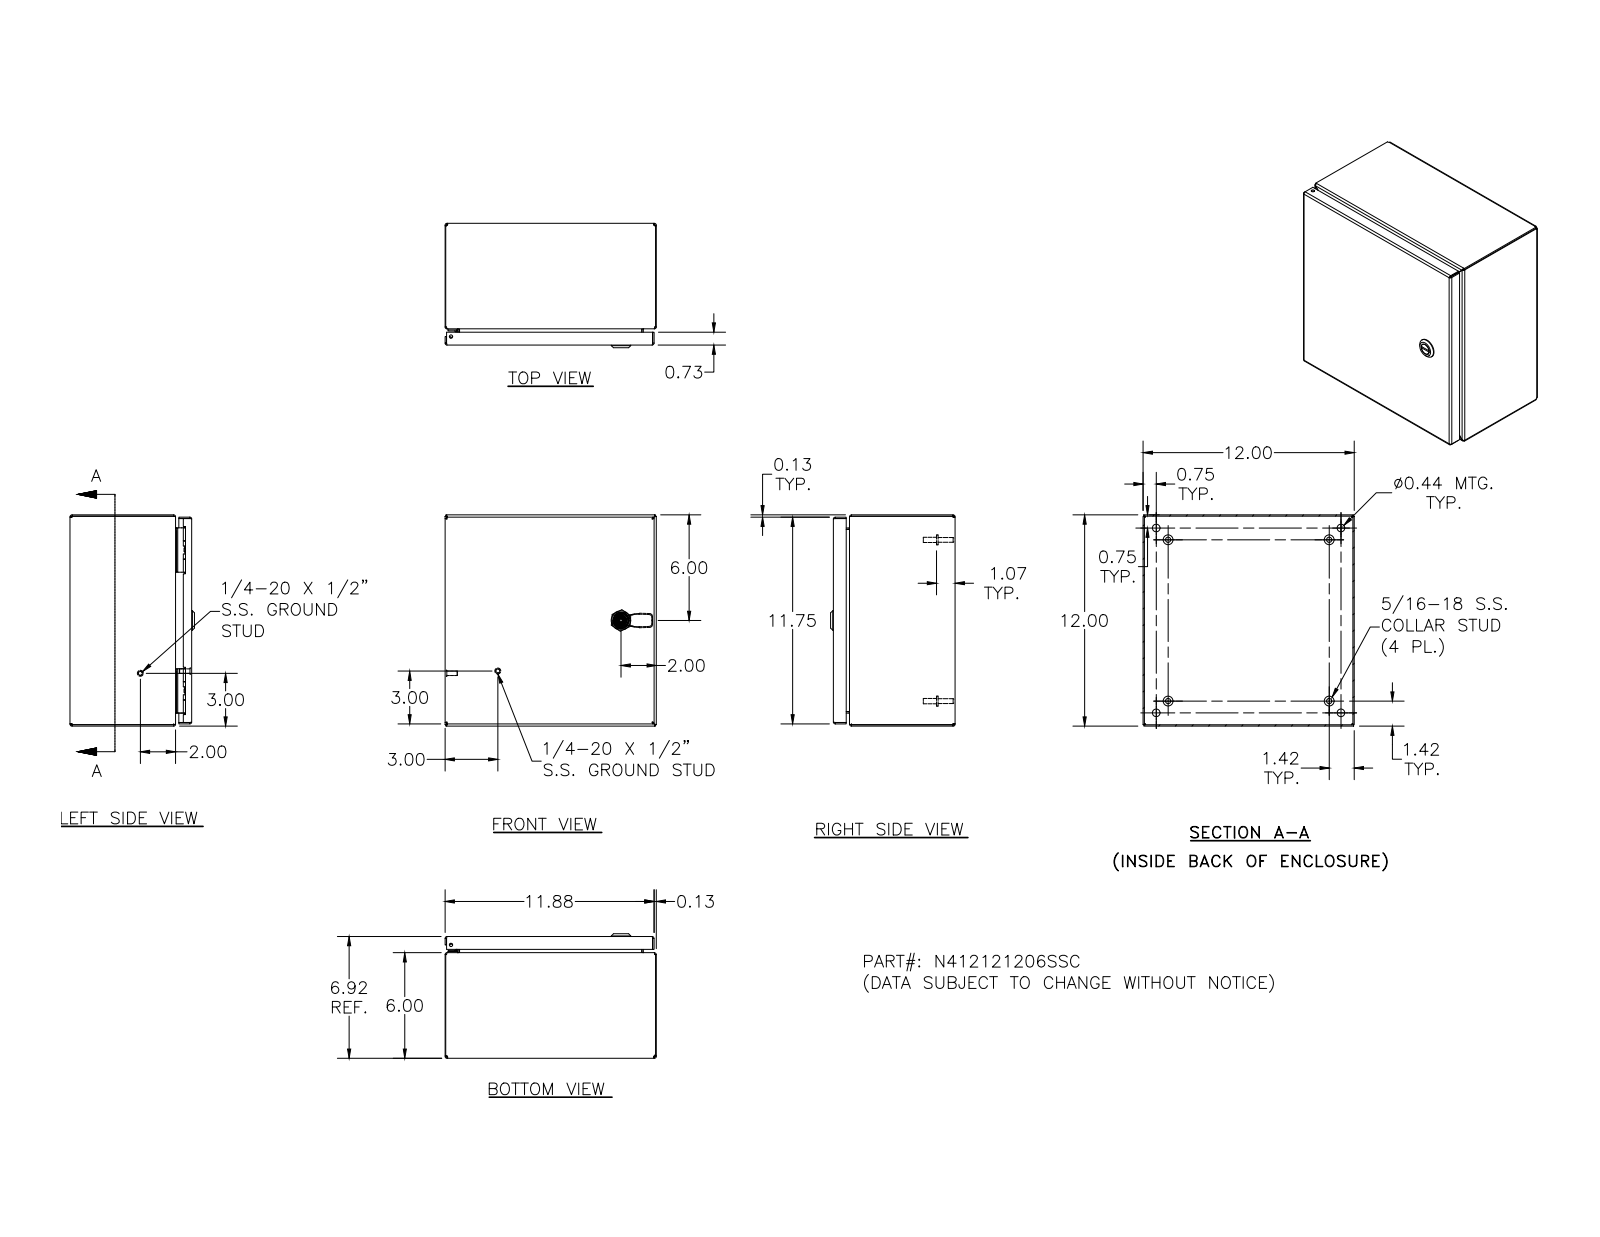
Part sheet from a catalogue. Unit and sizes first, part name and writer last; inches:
Units: inches
Overall size (bounding box): 12 × 12 × 7.075
Round holes (diameter × count): ⌀0.188 ×5, ⌀0.093 ×4, ⌀0.152 ×4, ⌀0.167 ×4, ⌀0.172 ×4, ⌀0.437 ×4, ⌀0.156 ×2, ⌀0.187 ×1, ⌀0.197 ×1, ⌀0.315 ×1, ⌀0.394 ×1, ⌀0.402 ×1
Round bosses / shafts (diameter × count): ⌀0.25 ×10, ⌀0.563 ×4, ⌀0.36 ×4, ⌀0.32 ×4, ⌀0.3 ×4, ⌀0.275 ×4, ⌀0.256 ×4, ⌀0.164 ×4
Partial cylindrical surfaces — rounded edges, fillets, slot ends (radius × count): R0.031 ×30, R0.05 ×26, R0.105 ×20, R0.016 ×18, R0.125 ×14, R0.02 ×9, R0.032 ×8, R0.07 ×8
Main face-to-face distances: 0.074, 11.926, 6.843, 11.852, 12, 6.769, 6.917, 5.926, 0.917, 11.187
Hole centre spacings: 8, 0.017, 0.66, 10.5, 0.019, 0.5, 0.648, 0.652
Volume: 50.58 in³ · Surface area: 1 381 in²
Bodies: 34 solids, 1384 faces (531 planar, 509 cylindrical, 344 other)
Part name (STEP PRODUCT): N412121206SSC; N412121206SSCBKP; 388151; N4121212SSCLID (+8 more)
STEP written by: Autodesk Inventor 2011 (AUTOMOTIVE_DESIGN)
